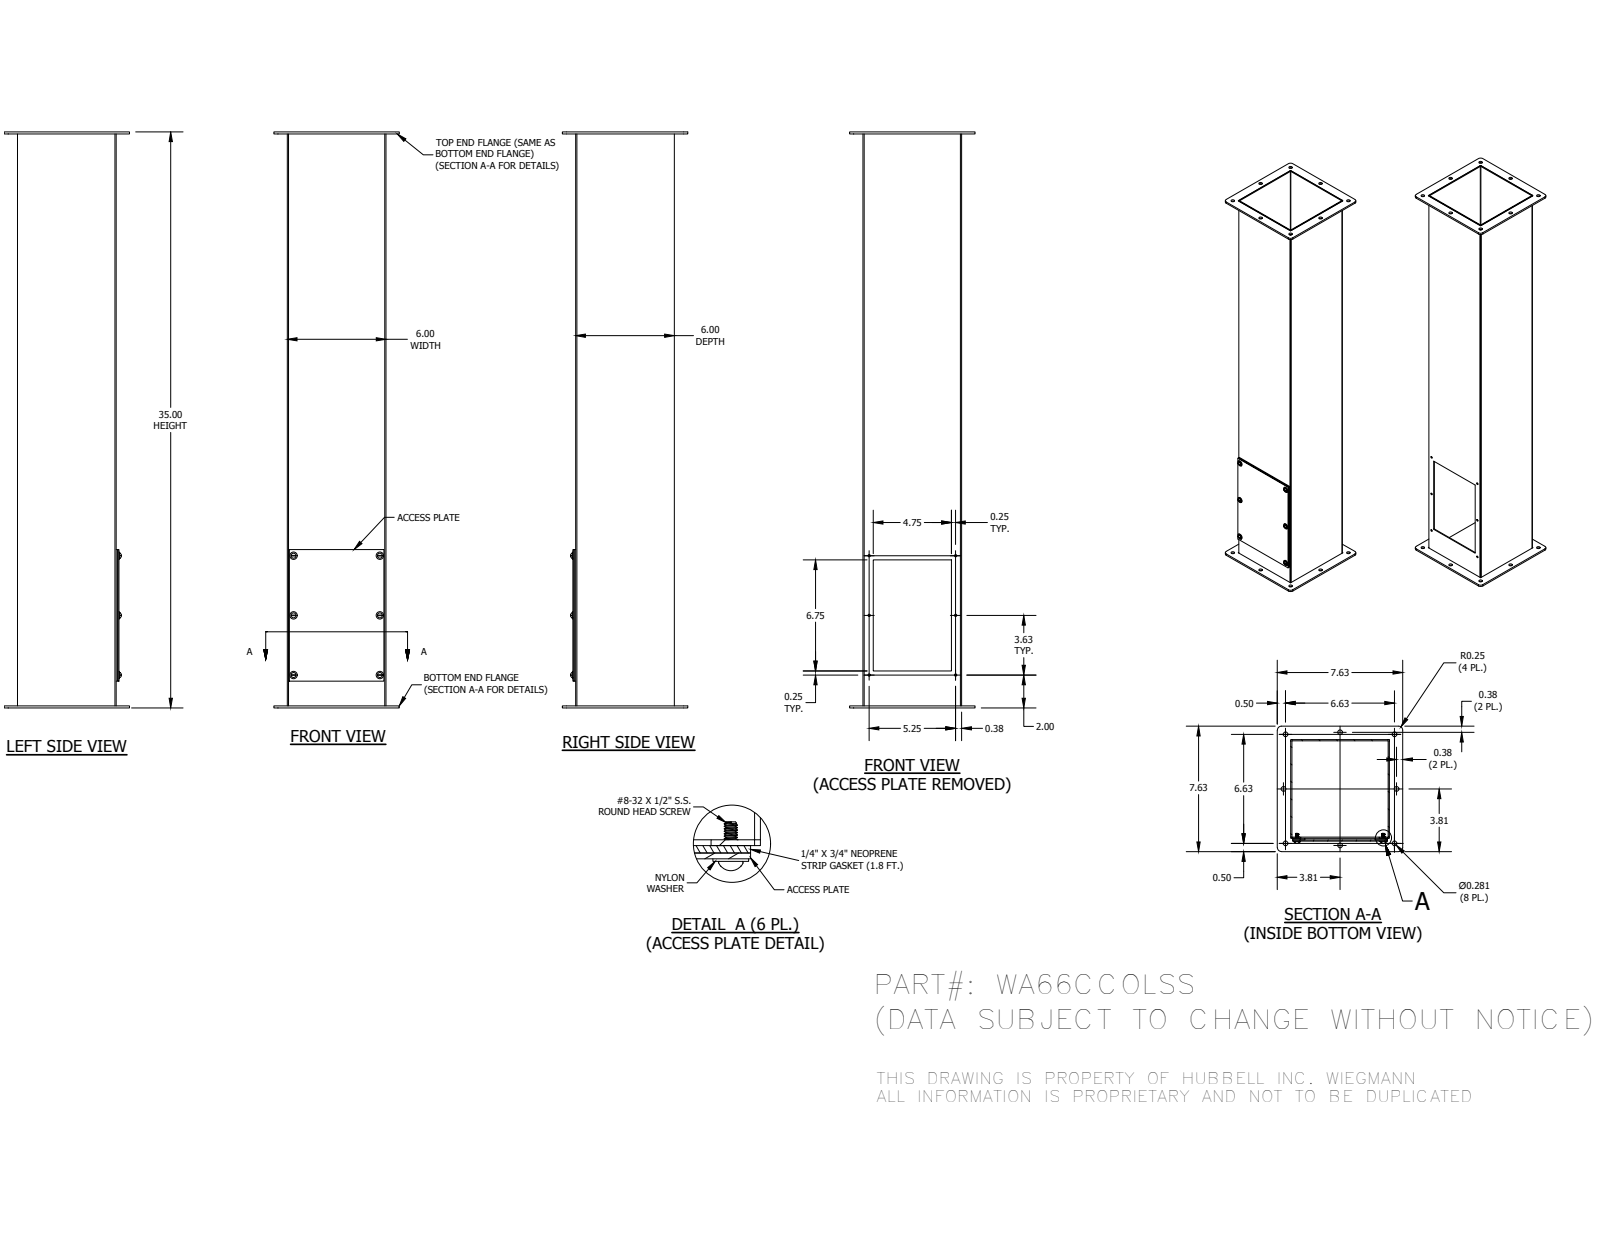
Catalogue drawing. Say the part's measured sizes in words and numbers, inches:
The part is named "WA66CCOLSSFRONT; WA66CCOLSSBLR; WA66CCOLSSBASERING; WA66CCOLSSCOVER (+4 more)". Its 3-D file was written by "Autodesk Inventor 2016 (AUTOMOTIVE_DESIGN)". It is 24 solids with 320 faces: 190 planar, 94 cylindrical and 36 other. Overall it measures 35 by 7.625 by 7.625 inches. Its volume is 69.08 cubic inches and its surface area 1 838 square inches. Round holes: 8 of diameter 0.281, 6 of diameter 0.14, 6 of diameter 0.25, 6 of diameter 0.278. Round bosses or shafts: 6 of diameter 0.453, 6 of diameter 0.309, 6 of diameter 0.164, 6 of diameter 0.123. Partial cylindrical surfaces (rounded edges, fillets, slot ends): 6 of radius 0.089, 4 of radius 0.25, 2 of radius 0.031, 2 of radius 0.105. The main face-to-face distances are 0.074, 5.926, 6, 5.852, 6.094, 0.168, 6.02, 0.094, 6.168, 0.242. The hole center spacings are 3.315, 7.519, 3.625, 3.625, 7.25, 4.861, 6.38, 6.38.
